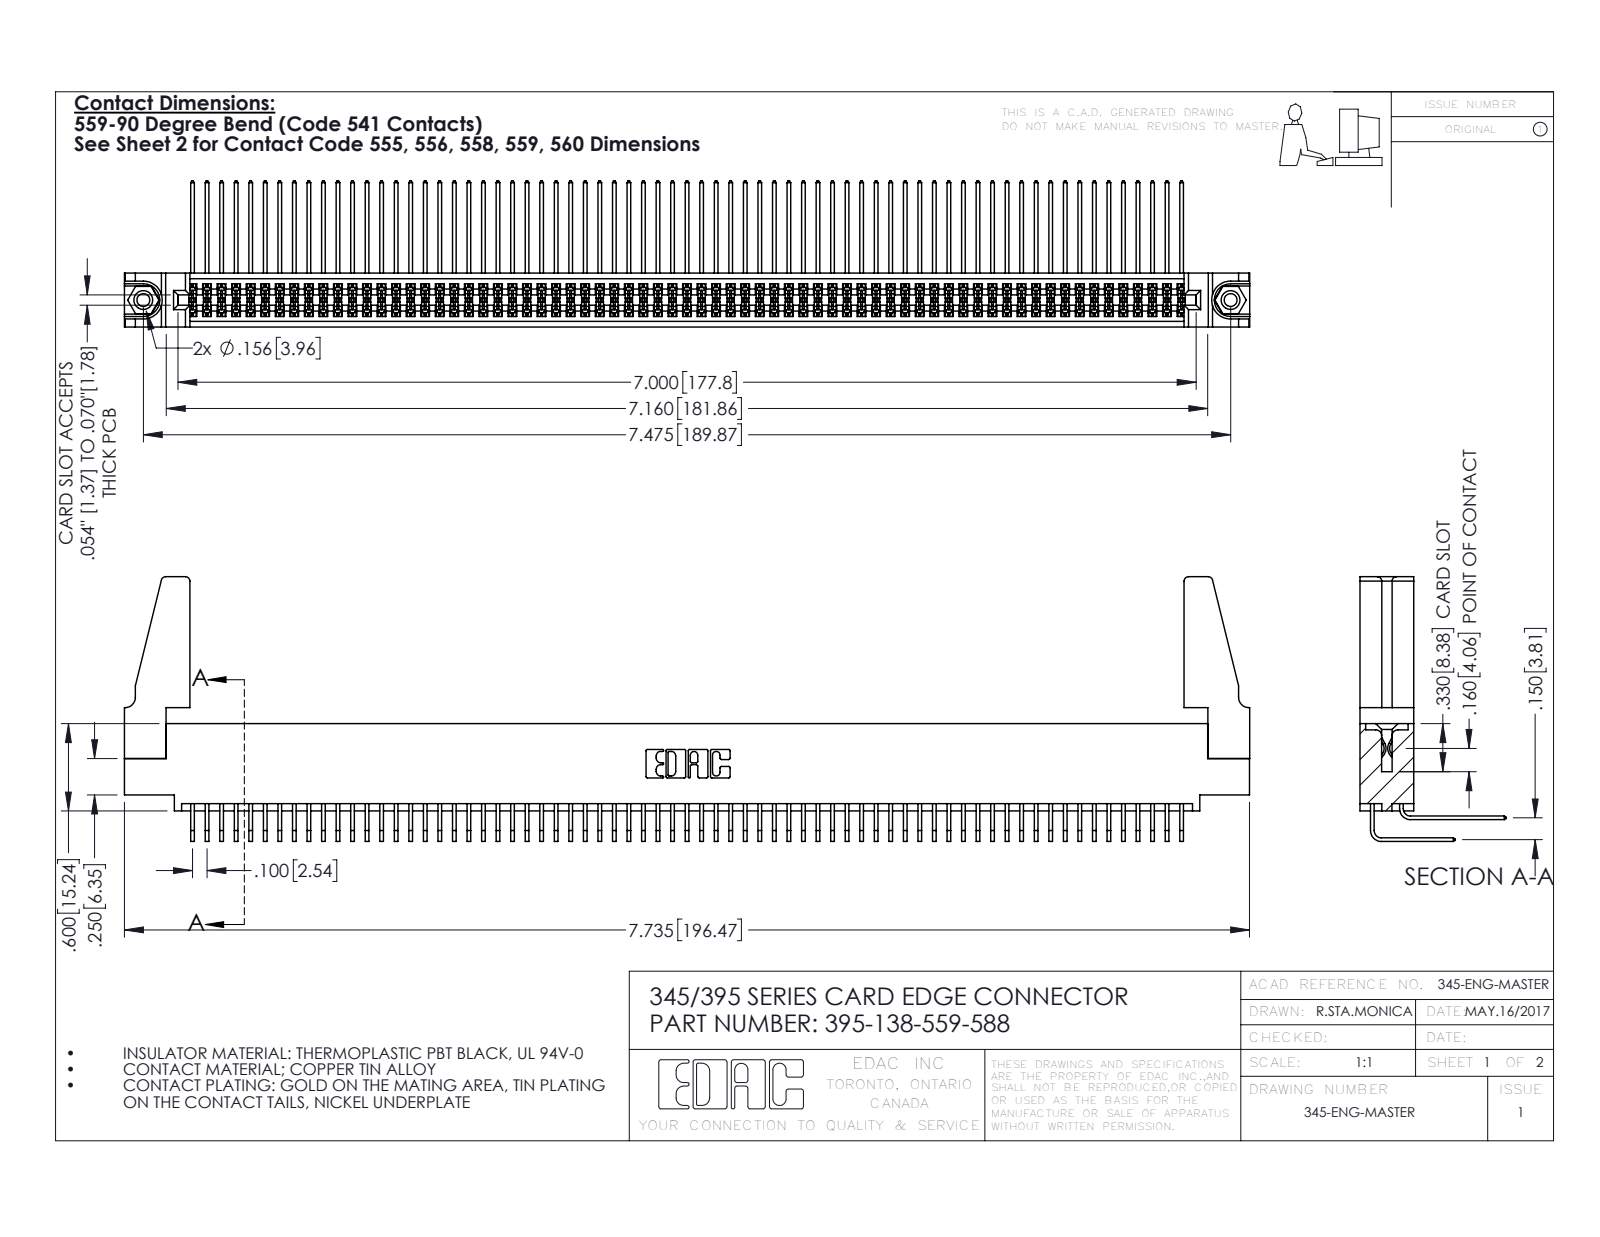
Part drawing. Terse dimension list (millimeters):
name: 395-138-559-588; 345-220-078_345-220-088; 345-292-001_559 Tail - 2; 345-250-001_345-250-001-102 (+2 more)
written by: SolidWorks 2016 (CONFIG_CONTROL_DESIGN)
unit: mm
bodies: 143 solids, 7430 faces (4986 planar, 2428 cylindrical, 16 other)
size: 196.5 × 46.2 × 25.5
volume: 23 320 mm³; area: 37 140 mm²
holes: 2× ⌀2.3, 2× ⌀3.2, 2× ⌀4, 1× ⌀1.6
bosses: 2× ⌀3.9
rounds: 275× R0.2, 22× R0.3, 8× R0.8, 6× R0.2, 6× R0.8, 3× R0.7, 2× R0.4, 2× R0.5
face distances: 1.8, 7.6, 9.4, 2.5, 6.9, 0.6, 5.1, 5.7, 4.4, 3.8
hole spacings: 6.9, 183.9, 189.9
